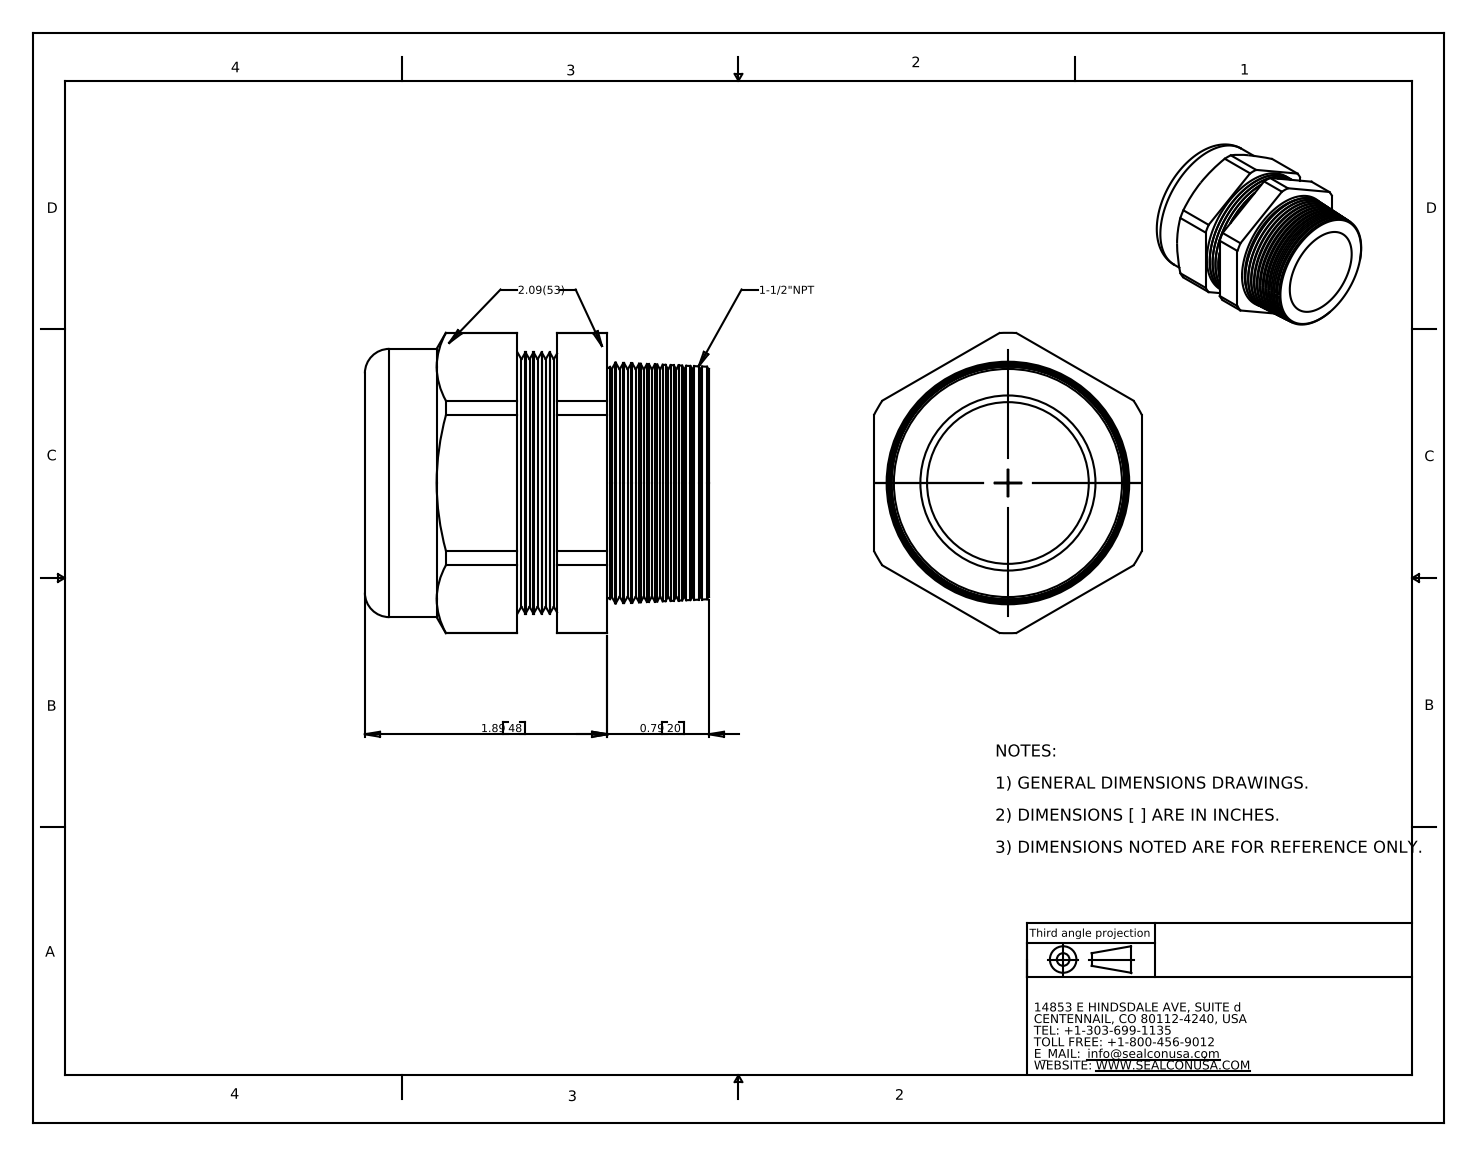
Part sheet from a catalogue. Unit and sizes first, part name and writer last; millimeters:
Units: millimetres
Overall size (bounding box): 68.1 × 59.5 × 53.1
Round holes (diameter × count): ⌀32 ×1, ⌀40.6 ×1
Round bosses / shafts (diameter × count): ⌀53.1 ×1, ⌀51.7 ×1
Partial cylindrical surfaces — rounded edges, fillets, slot ends (radius × count): R29.7 ×1
Main face-to-face distances: 53.1, 53.9, 33.8, 20.1, 13.7, 47.5, 67.6, 37.5, 23.8, 10
Volume: 85 070 mm³ · Surface area: 29 340 mm²
Bodies: 2 solids, 164 faces (20 planar, 32 cylindrical, 112 other)
Part name (STEP PRODUCT): CD36NA-GY
STEP written by: SolidWorks 2007 (CONFIG_CONTROL_DESIGN)
